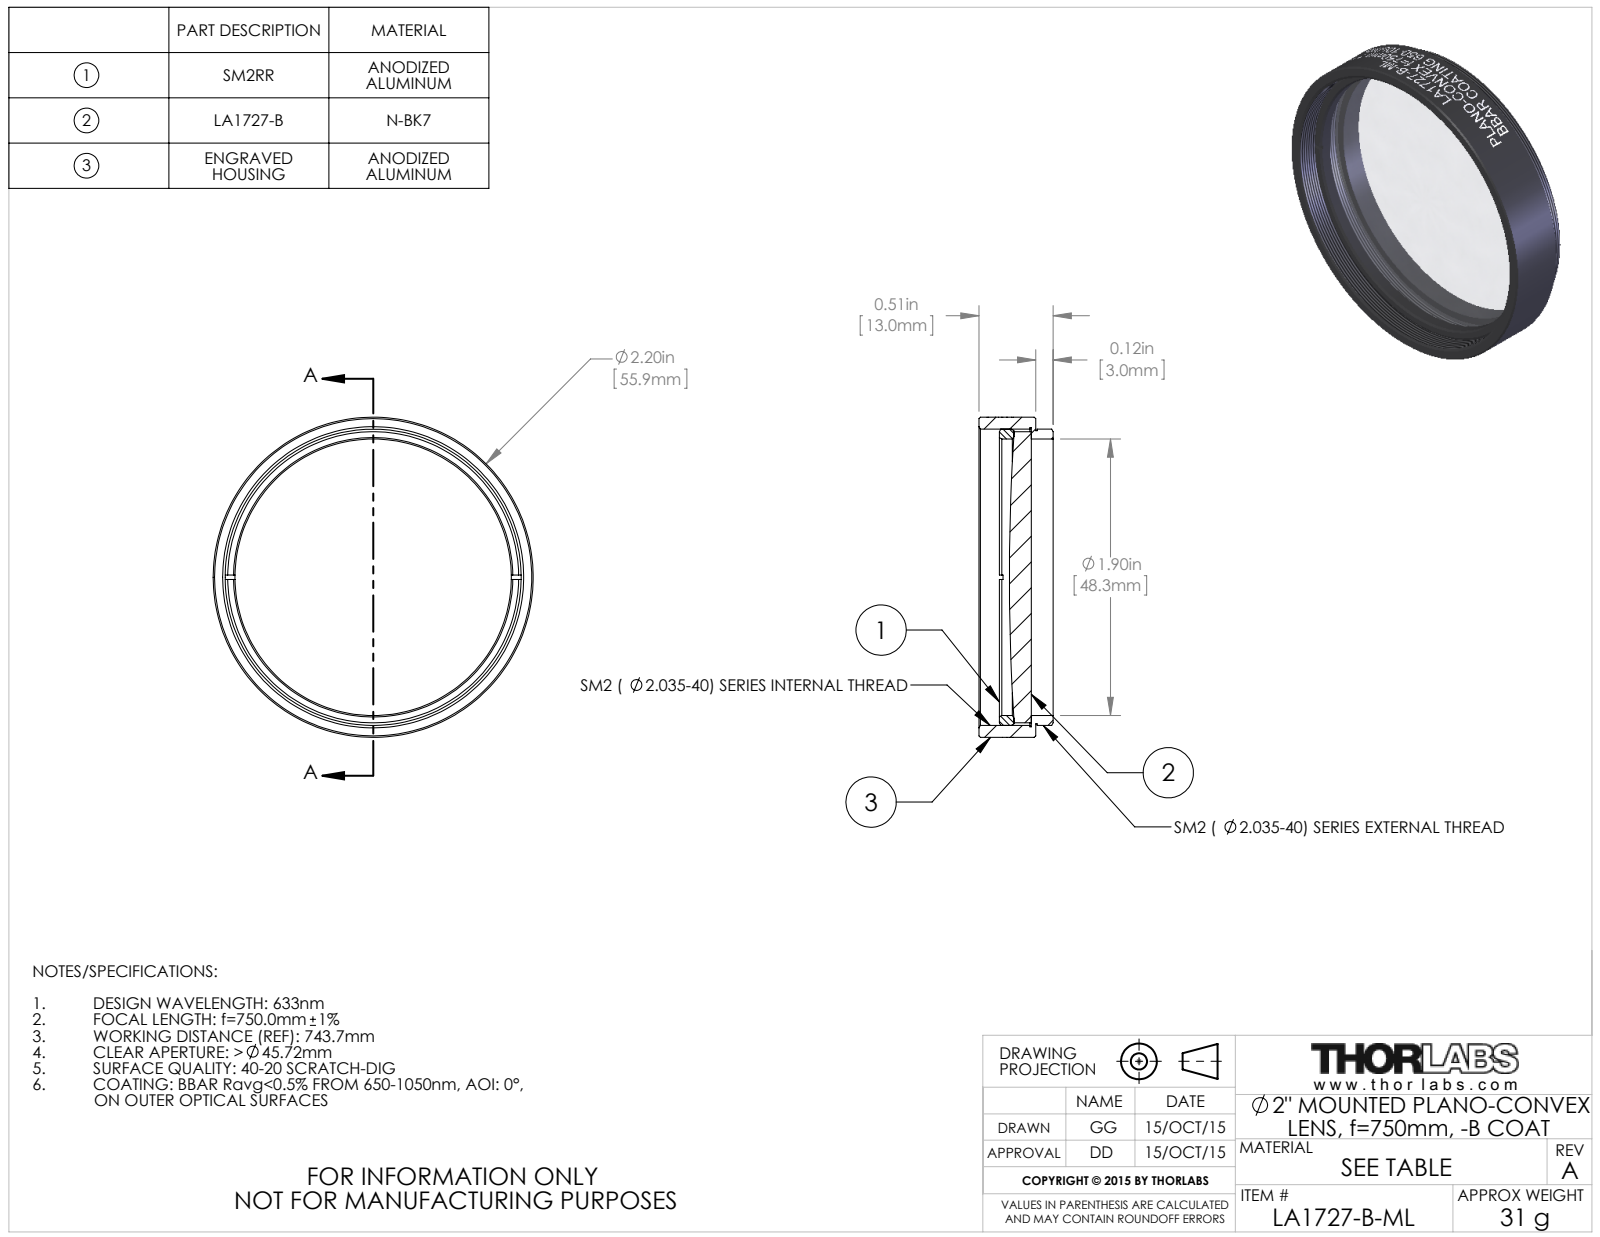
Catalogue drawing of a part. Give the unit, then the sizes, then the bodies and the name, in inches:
Units: inches
Overall size (bounding box): 2.2 × 2.2 × 0.51
Round holes (diameter × count): ⌀1.9 ×1, ⌀2.055 ×1
Round bosses / shafts (diameter × count): ⌀2.2 ×1, ⌀2.035 ×1, ⌀2.015 ×1, ⌀2 ×1
Main face-to-face distances: 0.12, 0.15, 0.03, 0.39, 0.36, 0.51, 0.27, 0.24, 0.37, 0.25
Volume: 0.735 in³ · Surface area: 17.59 in²
Bodies: 3 solids, 143 faces (16 planar, 107 cylindrical, 20 other)
Part name (STEP PRODUCT): TTN039624-E0W
STEP written by: SolidWorks 2014 (CONFIG_CONTROL_DESIGN)
